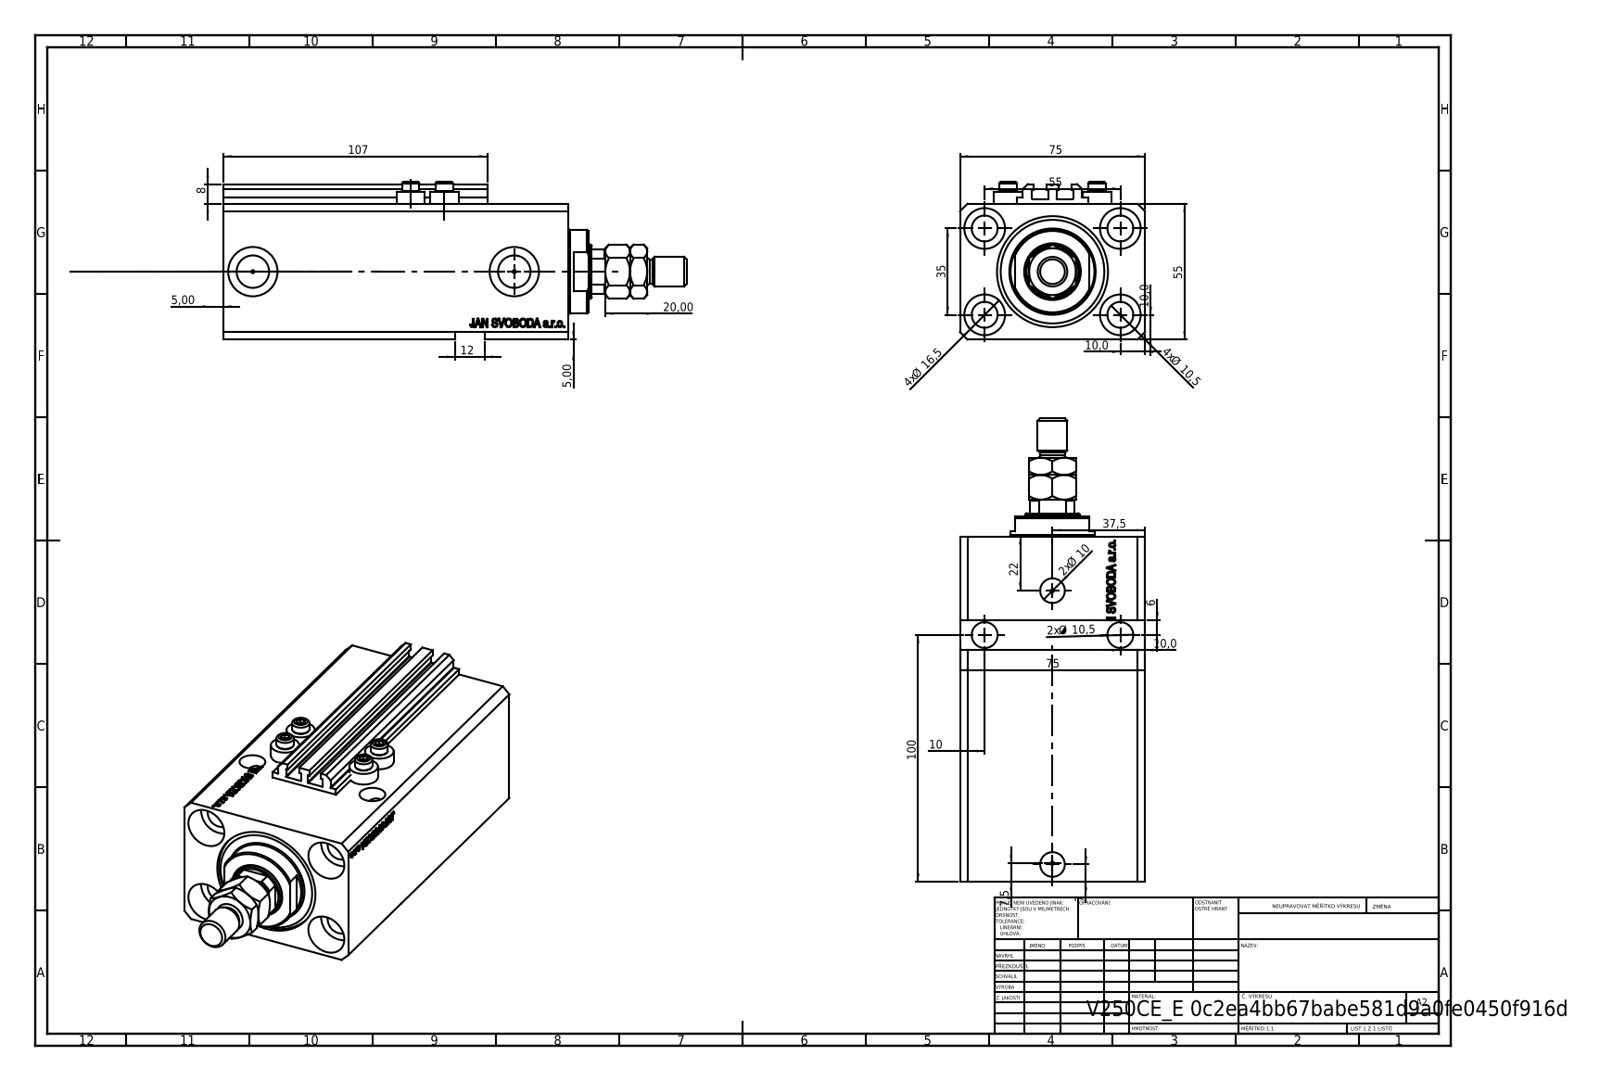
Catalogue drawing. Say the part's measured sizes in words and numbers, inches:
The part is named "MTA; V250CE_E_Body; V250CE_VC_E; V250CE_C_VCP (+1 more)". Its 3-D file was written by "SolidWorks 2019 (CONFIG_CONTROL_DESIGN)". It is 9 solids with 1113 faces: 529 planar, 130 cylindrical and 454 other. Overall it measures 7.398 by 2.953 by 2.52 inches. Its volume is 30.43 cubic inches and its surface area 184 square inches. Round holes: 7 of diameter 0.413, 4 of diameter 0.049, 4 of diameter 0.157, 4 of diameter 0.65, 2 of diameter 0.394, 2 of diameter 0.518, 2 of diameter 0.787, 1 of diameter 0.866, 1 of diameter 1.26, 1 of diameter 1.772. Round bosses or shafts: 4 of diameter 0.457, 4 of diameter 0.276, 1 of diameter 1.339, 1 of diameter 0.472, 1 of diameter 0.394. Partial cylindrical surfaces (rounded edges, fillets, slot ends): 10 of radius 0.008, 1 of radius 0.413. The main face-to-face distances are 2.165, 2.953, 5.512, 4.445, 1.067, 0.098, 0.39, 0.118, 2.244, 4.055. The hole center spacings are 1.283, 2.165, 0.535, 0.555, 1.016, 1.294, 1.324, 1.378.
